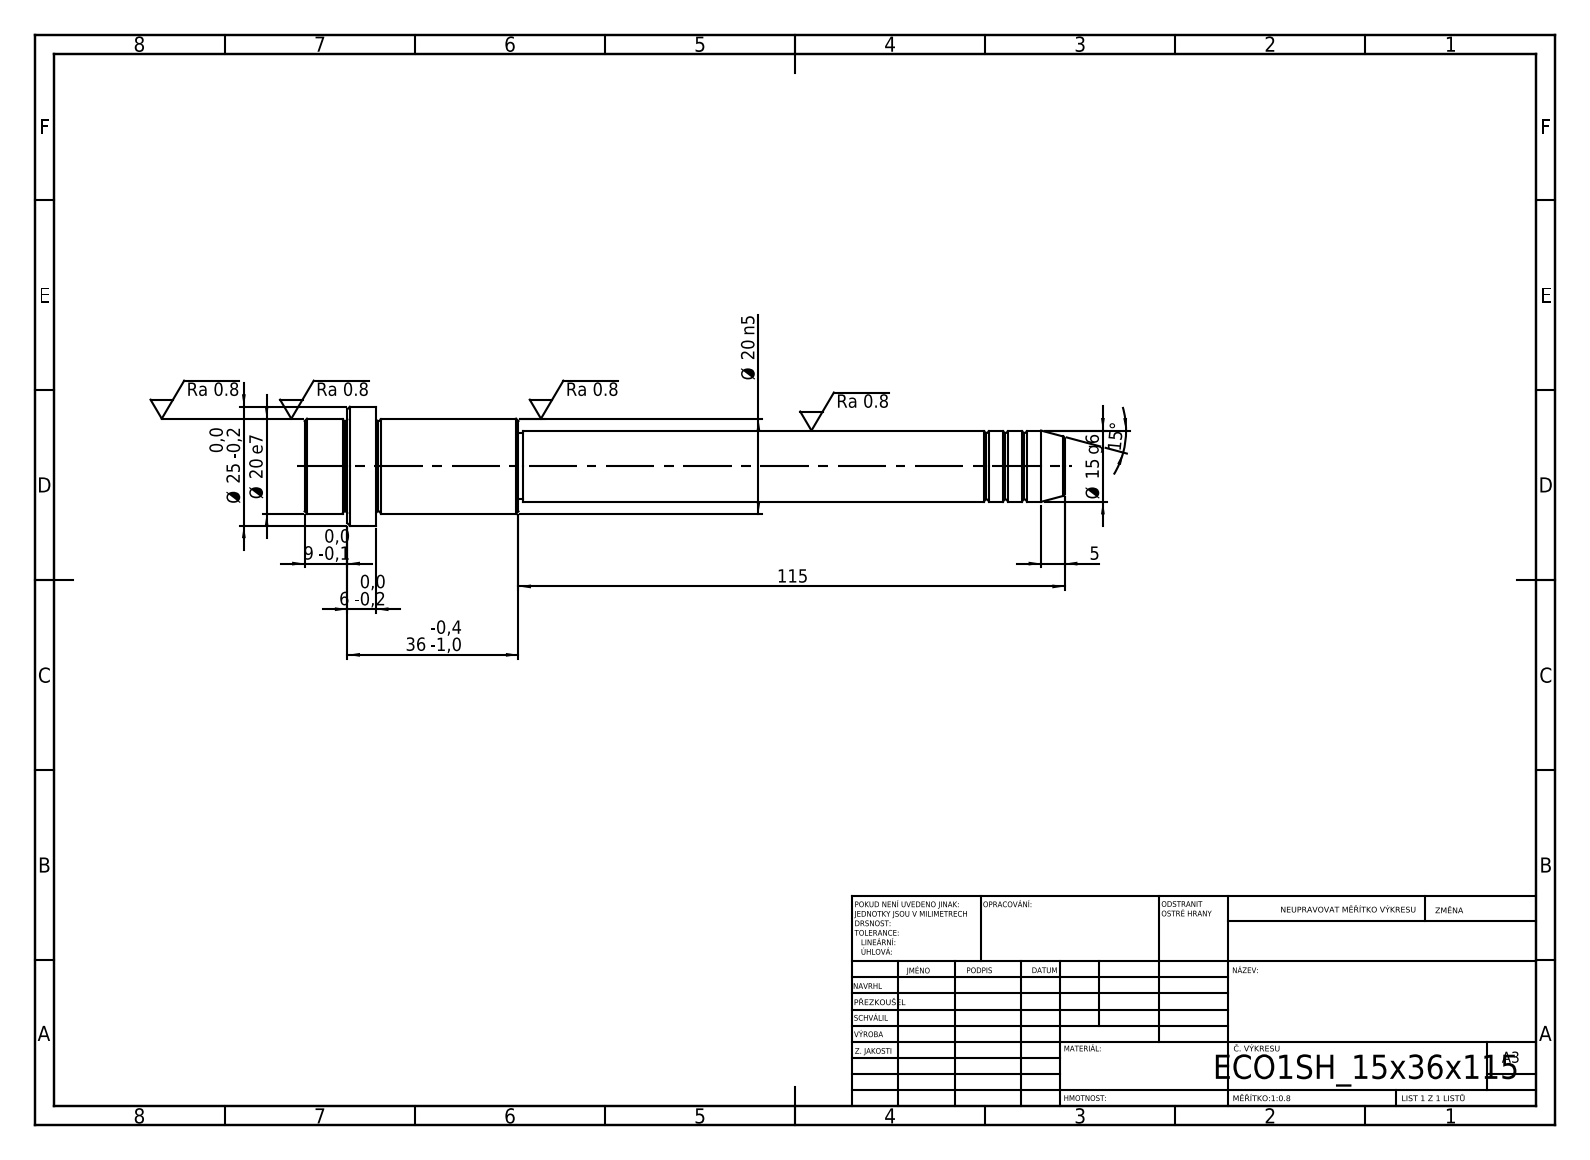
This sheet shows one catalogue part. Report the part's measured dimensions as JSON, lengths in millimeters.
{"step_written_by": "SolidWorks 2019 (CONFIG_CONTROL_DESIGN)", "units": "millimeters", "bodies": {"solids": 1, "faces": 52, "planar": 6, "cylindrical": 16, "other": 30}, "overall_size": [160, 25, 25], "volume_mm3": 35220, "surface_area_mm2": 9366, "round_bosses_or_shafts": [[25, 1], [20, 1], [15, 1], [14, 1]], "face_to_face_distances": [15, 6, 9, 30, 36, 45, 115, 145, 151, 160]}
